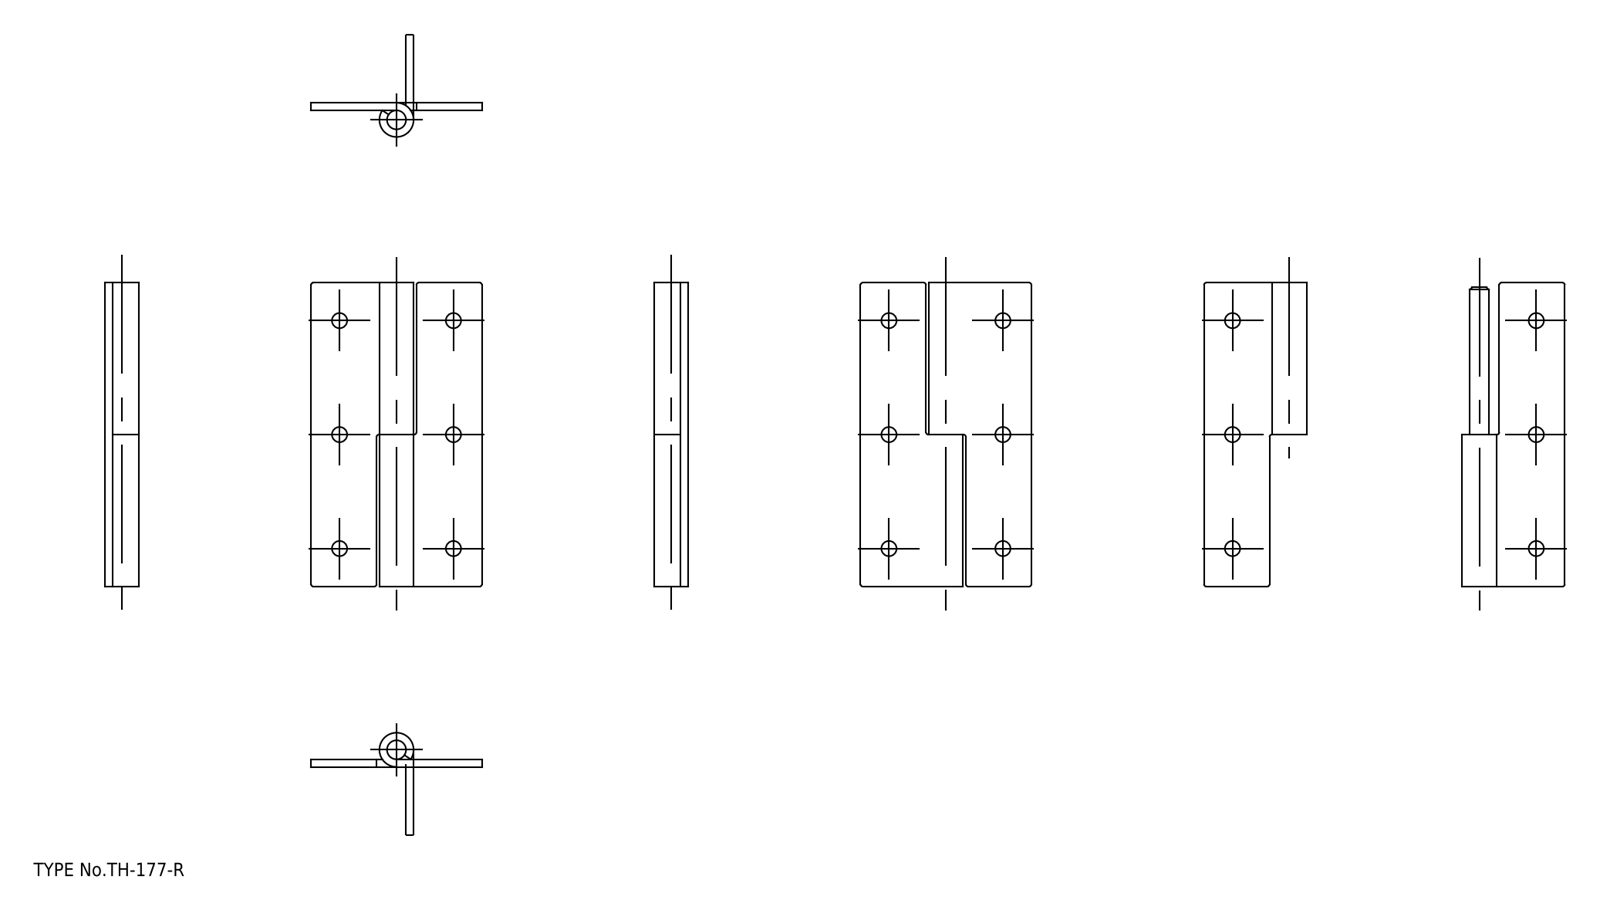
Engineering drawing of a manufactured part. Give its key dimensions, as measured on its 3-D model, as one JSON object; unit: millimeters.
{"step_written_by": "spGate 17.5.2 (AUTOMOTIVE_DESIGN)", "units": "millimeters", "bodies": {"solids": 3, "faces": 46, "planar": 18, "cylindrical": 26, "other": 2}, "overall_size": [64, 36, 7.2], "volume_mm3": 5489, "surface_area_mm2": 7399, "round_holes": [[3.2, 6], [4, 1]], "round_bosses_or_shafts": [[7.2, 1]], "partial_cylinders_radius": [[0.5, 8]], "face_to_face_distances": [1.6, 32, 36, 13.8, 22.2, 64, 8.4, 63, 31, 1], "hole_center_spacings": [24, 33.94, 48, 53.67]}
